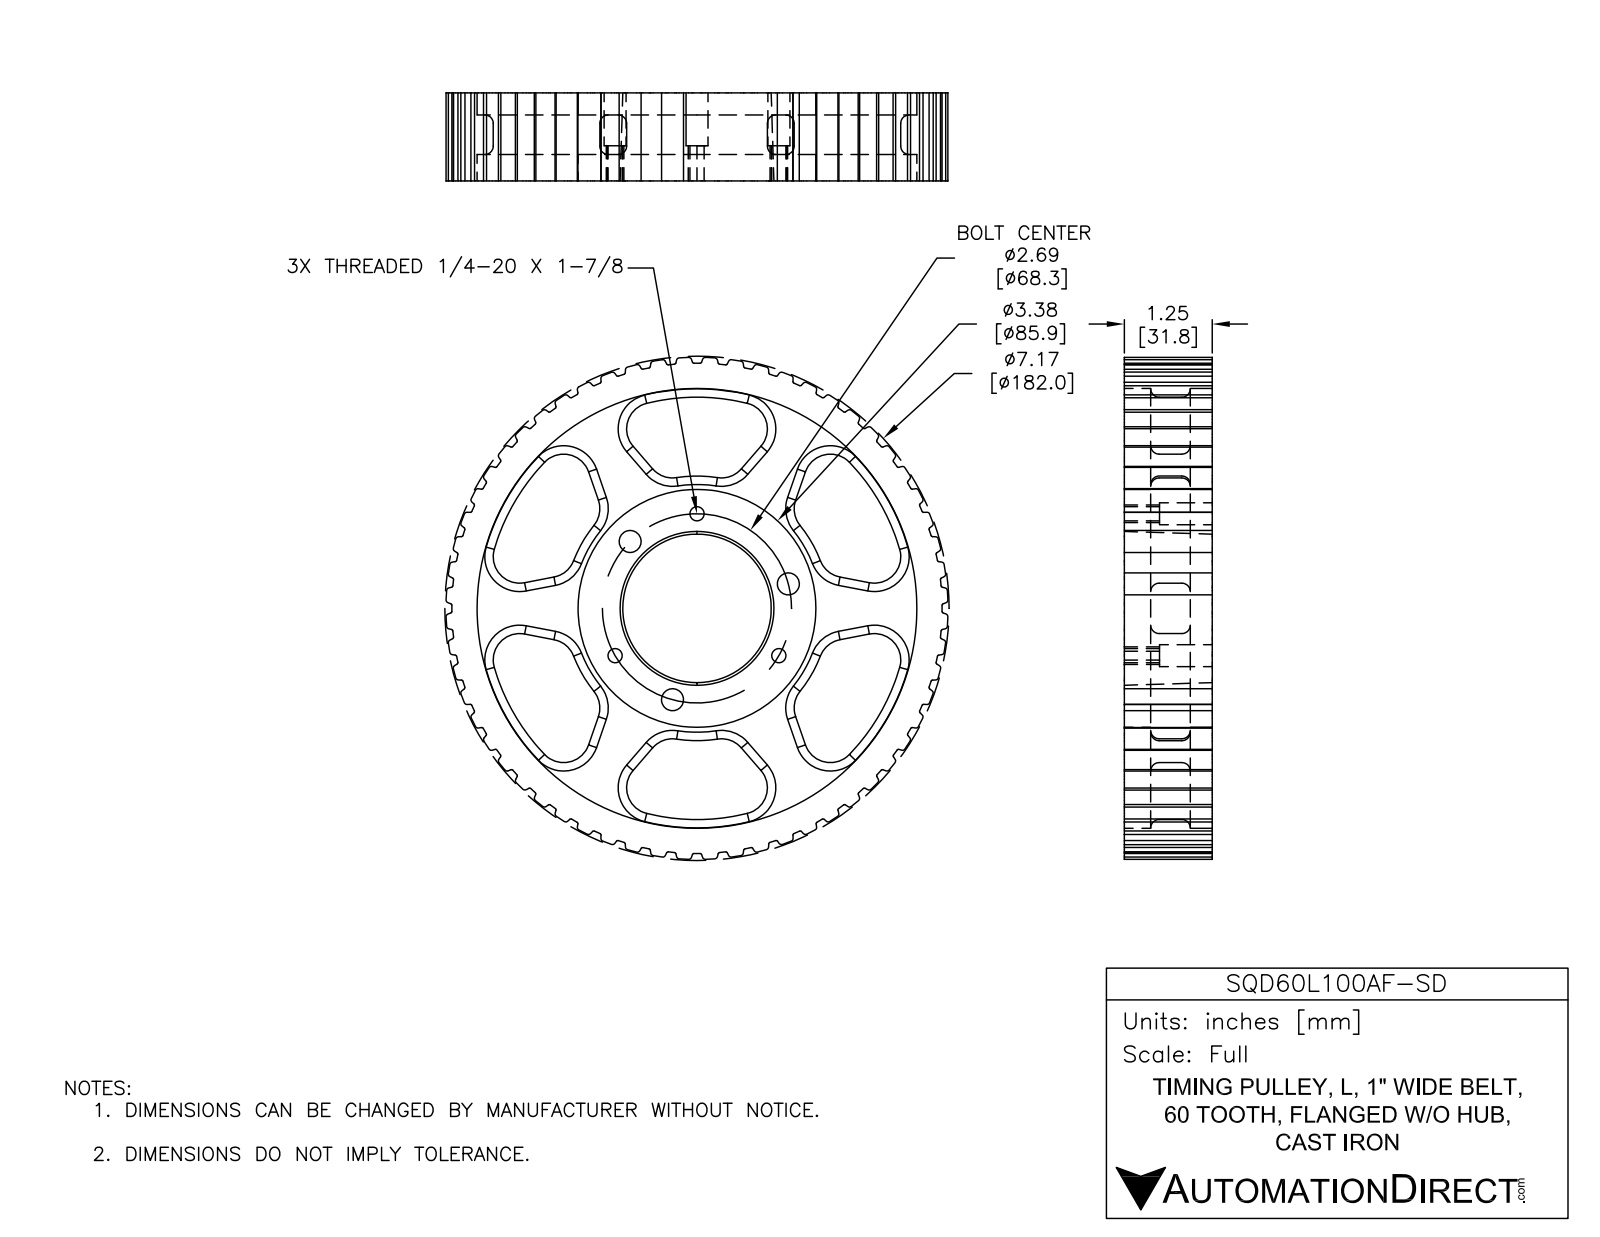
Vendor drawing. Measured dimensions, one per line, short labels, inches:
name: SQD60L100AF-SD
written by: SolidWorks 2014 (AUTOMOTIVE_DESIGN)
unit: in
bodies: 1 solid, 725 faces (201 planar, 438 cylindrical, 86 other)
size: 7.131 × 7.131 × 1.25
volume: 22.59 in³; area: 133.6 in²
holes: 6× ⌀0.313, 3× ⌀0.201, 1× ⌀6.25
bosses: 1× ⌀3.38
rounds: 120× R0.021, 120× R0.04, 24× R0.12, 24× R0.375, 1× R1.88, 1× R3, 1× R3.568
face distances: 1.25, 0.313, 0.937, 0.875, 0.562, 0.375, 6.967, 6.971, 2.27, 2.271
hole spacings: 1.344, 2.327, 2.328, 2.665, 1.028, 1.636, 1.029, 1.343
